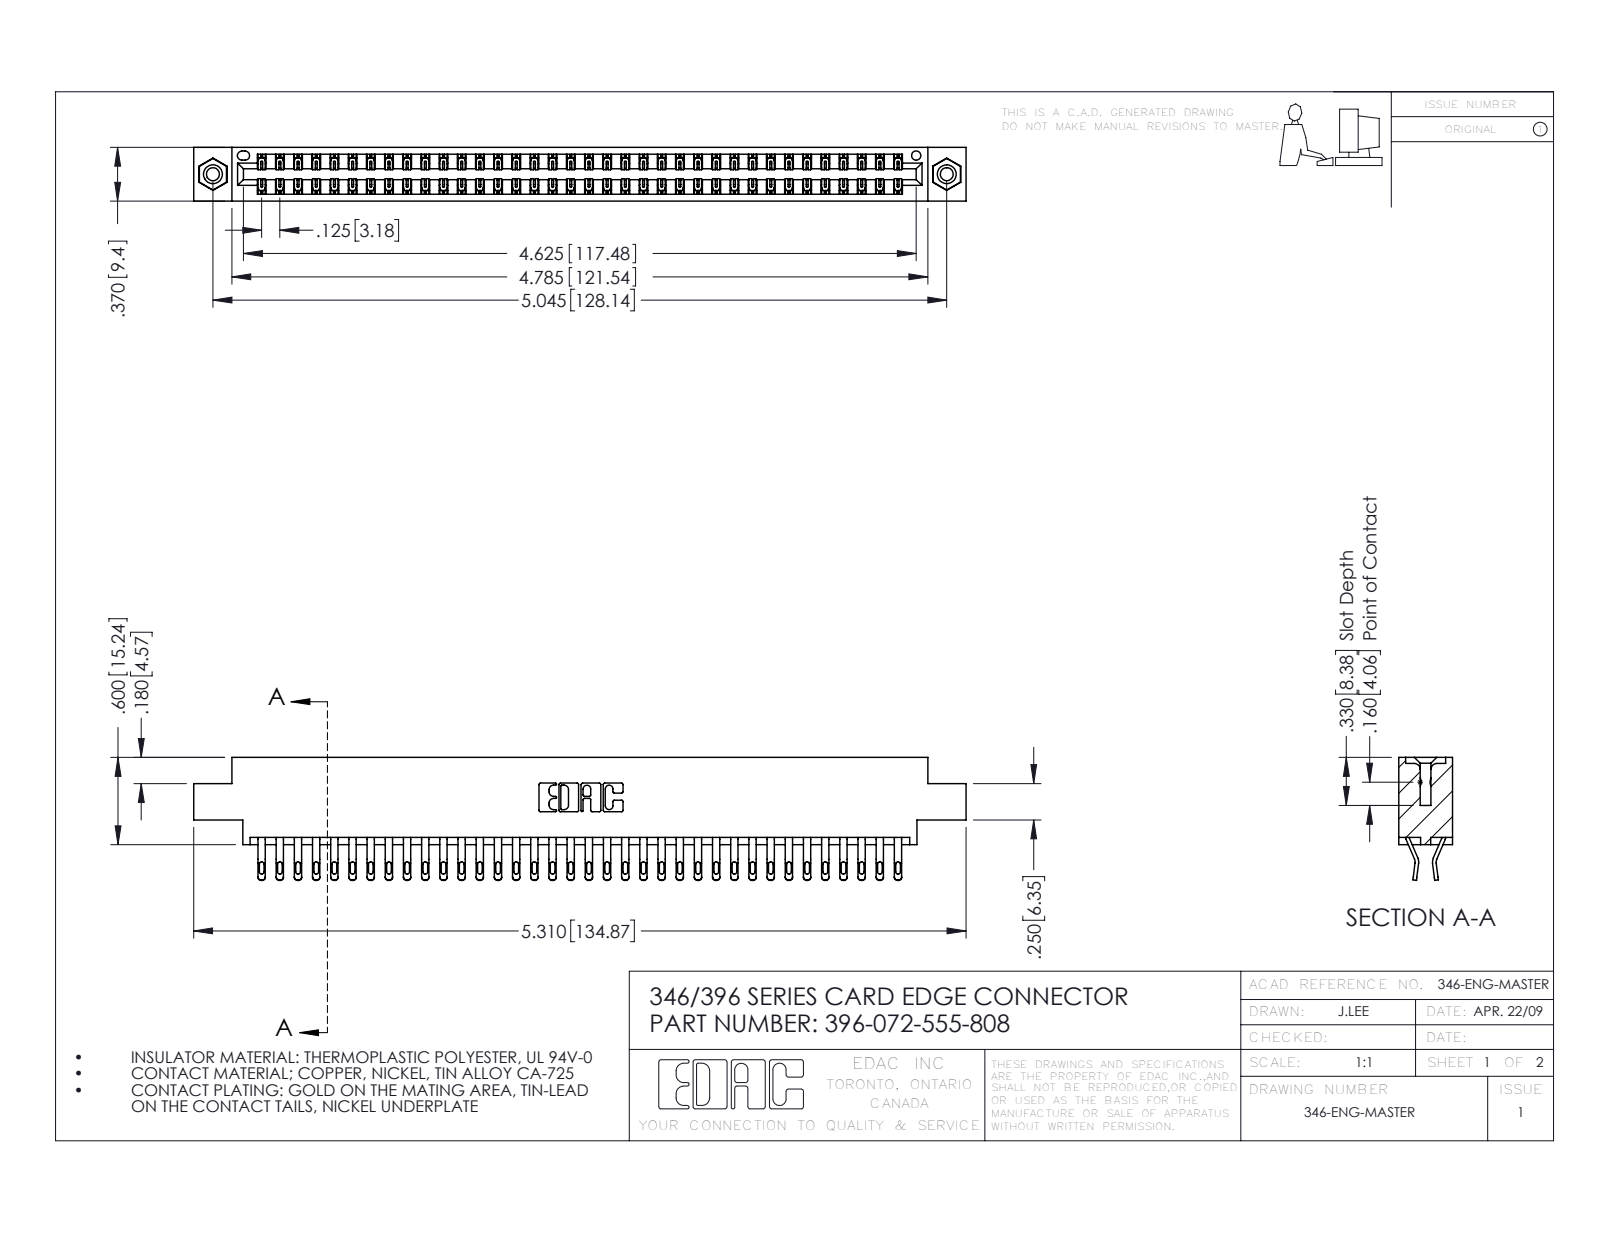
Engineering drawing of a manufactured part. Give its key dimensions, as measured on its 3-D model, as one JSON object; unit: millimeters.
{"part_name": "345-250-001_345-250-003-102; 346 Part_0.170 Offset - 0.156 Dia-TI; 396-072-555-808; 345-292-001_555 Tail", "step_written_by": "SolidWorks 2016 (CONFIG_CONTROL_DESIGN)", "units": "millimeters", "bodies": {"solids": 75, "faces": 4362, "planar": 2488, "cylindrical": 1858, "other": 16}, "overall_size": [134.9, 21.5, 9.4], "volume_mm3": 13200, "surface_area_mm2": 18930, "round_holes": [[2.3, 2], [3.2, 2], [4, 2], [1.6, 1]], "round_bosses_or_shafts": [[3.9, 2]], "partial_cylinders_radius": [[0.4, 144], [0.5, 144], [0.2, 108], [0.3, 22], [0.2, 6], [0.8, 6], [0.7, 3], [0.3, 2]], "face_to_face_distances": [1.2, 8.2, 9.4, 6.4, 0.6, 1.8, 7.6, 7, 5.6, 3.8], "hole_center_spacings": [6.2, 122.8, 128.1]}
